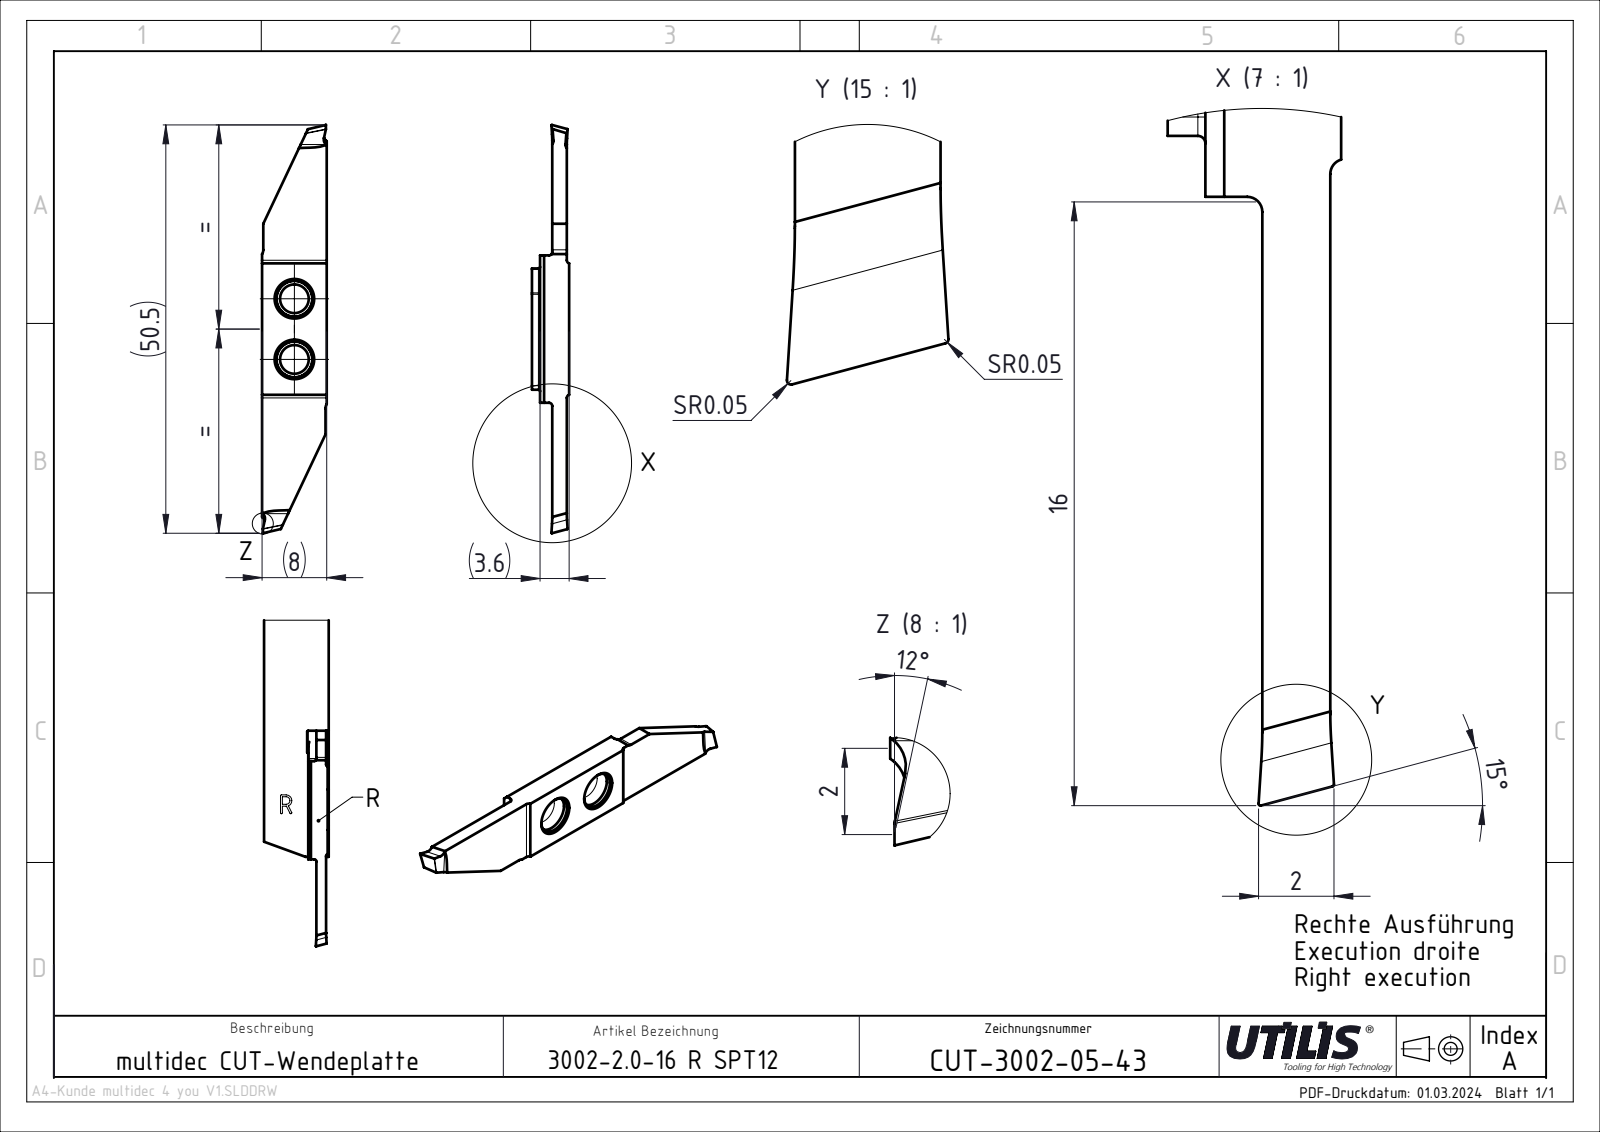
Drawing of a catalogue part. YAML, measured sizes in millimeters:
part_name: "CUT-3002 SPT Slim_and_Deep; ASME Y14.5"
step_written_by: "SolidWorks 2023 SP4 || FormatWorks Professional (AP242_MANAGED_MODEL_BASED_3D_ENGINEERING_MIM_LF)"
units: millimeters
bodies: {solids: 1, faces: 36, planar: 22, cylindrical: 14, other: 0}
overall_size: [50.5, 8, 3.6]
volume: 774
surface_area: 967
round_holes:
  - {diameter: 3.55, count: 2}
partial_cylinders:
  - {radius: 0.4, count: 4}
  - {radius: 1, count: 2}
face_to_face_distances: [1.8, 2.09, 1.51, 3.31, 3.6, 8, 18.09, 7.85, 18.22, 7.7]
hole_center_spacings: [7.5]
